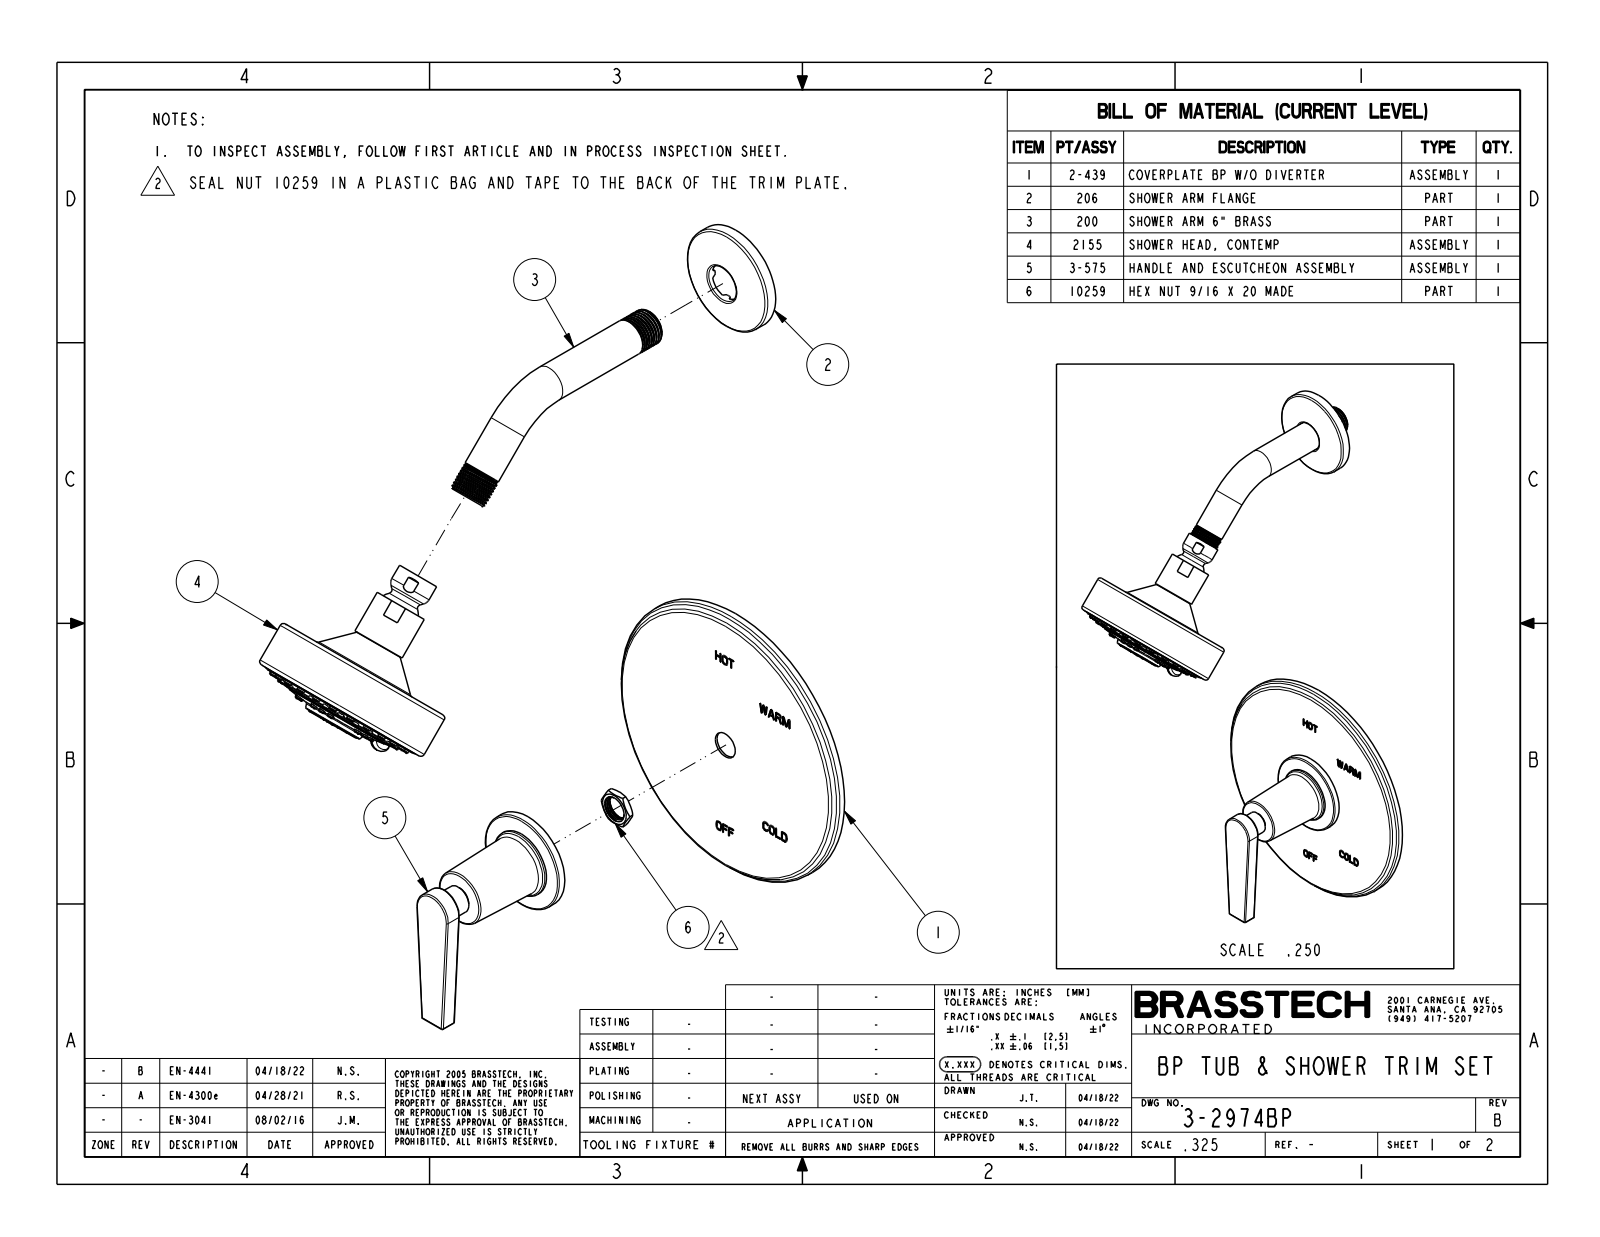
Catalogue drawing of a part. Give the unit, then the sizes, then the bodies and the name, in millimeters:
Units: millimetres
Overall size (bounding box): 417.6 × 207.6 × 165.1
Round holes (diameter × count): ⌀1.5 ×8, ⌀11.8 ×1, ⌀23.5 ×1
Round bosses / shafts (diameter × count): ⌀3.6 ×39, ⌀4.2 ×23, ⌀20.7 ×4, ⌀165.1 ×1, ⌀101.6 ×1, ⌀94.6 ×1, ⌀60.5 ×1, ⌀59 ×1
Partial cylindrical surfaces — rounded edges, fillets, slot ends (radius × count): R0.8 ×8, R2 ×8, R0.5 ×2, R3.5 ×1, R11.7 ×1, R12 ×1, R13 ×1, R16 ×1
Main face-to-face distances: 8, 4.7, 12.7, 80.8, 72.9, 68.1, 71.3, 63.4, 58.6, 9.5
Hole centre spacings: 11.3, 14.7, 20.8, 20.8, 27.2, 11.3, 14.7, 27.2
Volume: 572 200 mm³ · Surface area: 104 800 mm²
Bodies: 2 solids, 1431 faces (471 planar, 215 cylindrical, 745 other)
Part name (STEP PRODUCT): MSBR-2; MSBR-1; ASM0001_ASM
STEP written by: CREO PARAMETRIC BY PTC INC, 2018400 (CONFIG_CONTROL_DESIGN)
